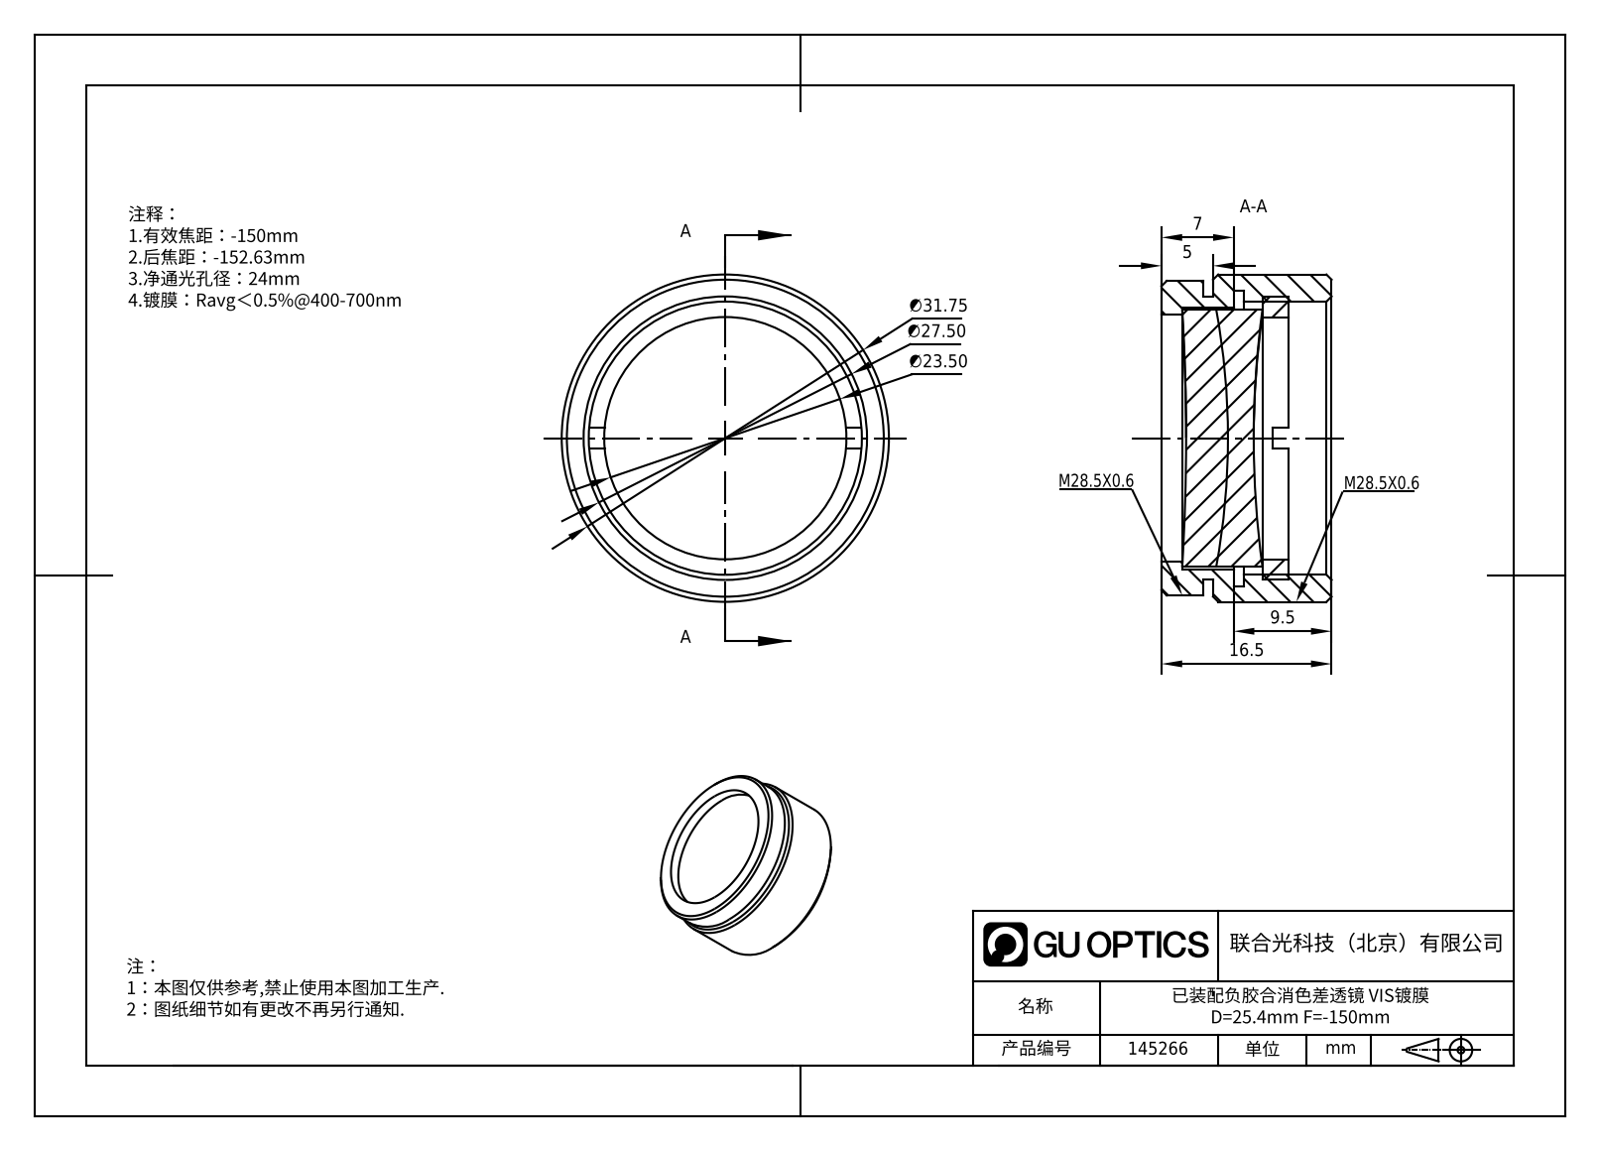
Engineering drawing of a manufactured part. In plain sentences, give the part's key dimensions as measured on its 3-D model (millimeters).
The part is named "145266". Its 3-D file was written by "SolidWorks 2020 (CONFIG_CONTROL_DESIGN)". It is 4 solids with 54 faces: 16 planar, 22 cylindrical and 16 other. Overall it measures 31.75 by 31.75 by 16.5 millimeters. Its volume is 7 712 cubic millimeters and its surface area 7 303 square millimeters. Round holes: 1 of diameter 23.5, 1 of diameter 24, 1 of diameter 25.4, 1 of diameter 26.5, 1 of diameter 28.7. Round bosses or shafts: 1 of diameter 31.75, 1 of diameter 30.5, 1 of diameter 27.5, 1 of diameter 25. The main face-to-face distances are 3, 2, 1, 4, 5, 9.8, 12.3, 2.5, 16.5, 6.7.
